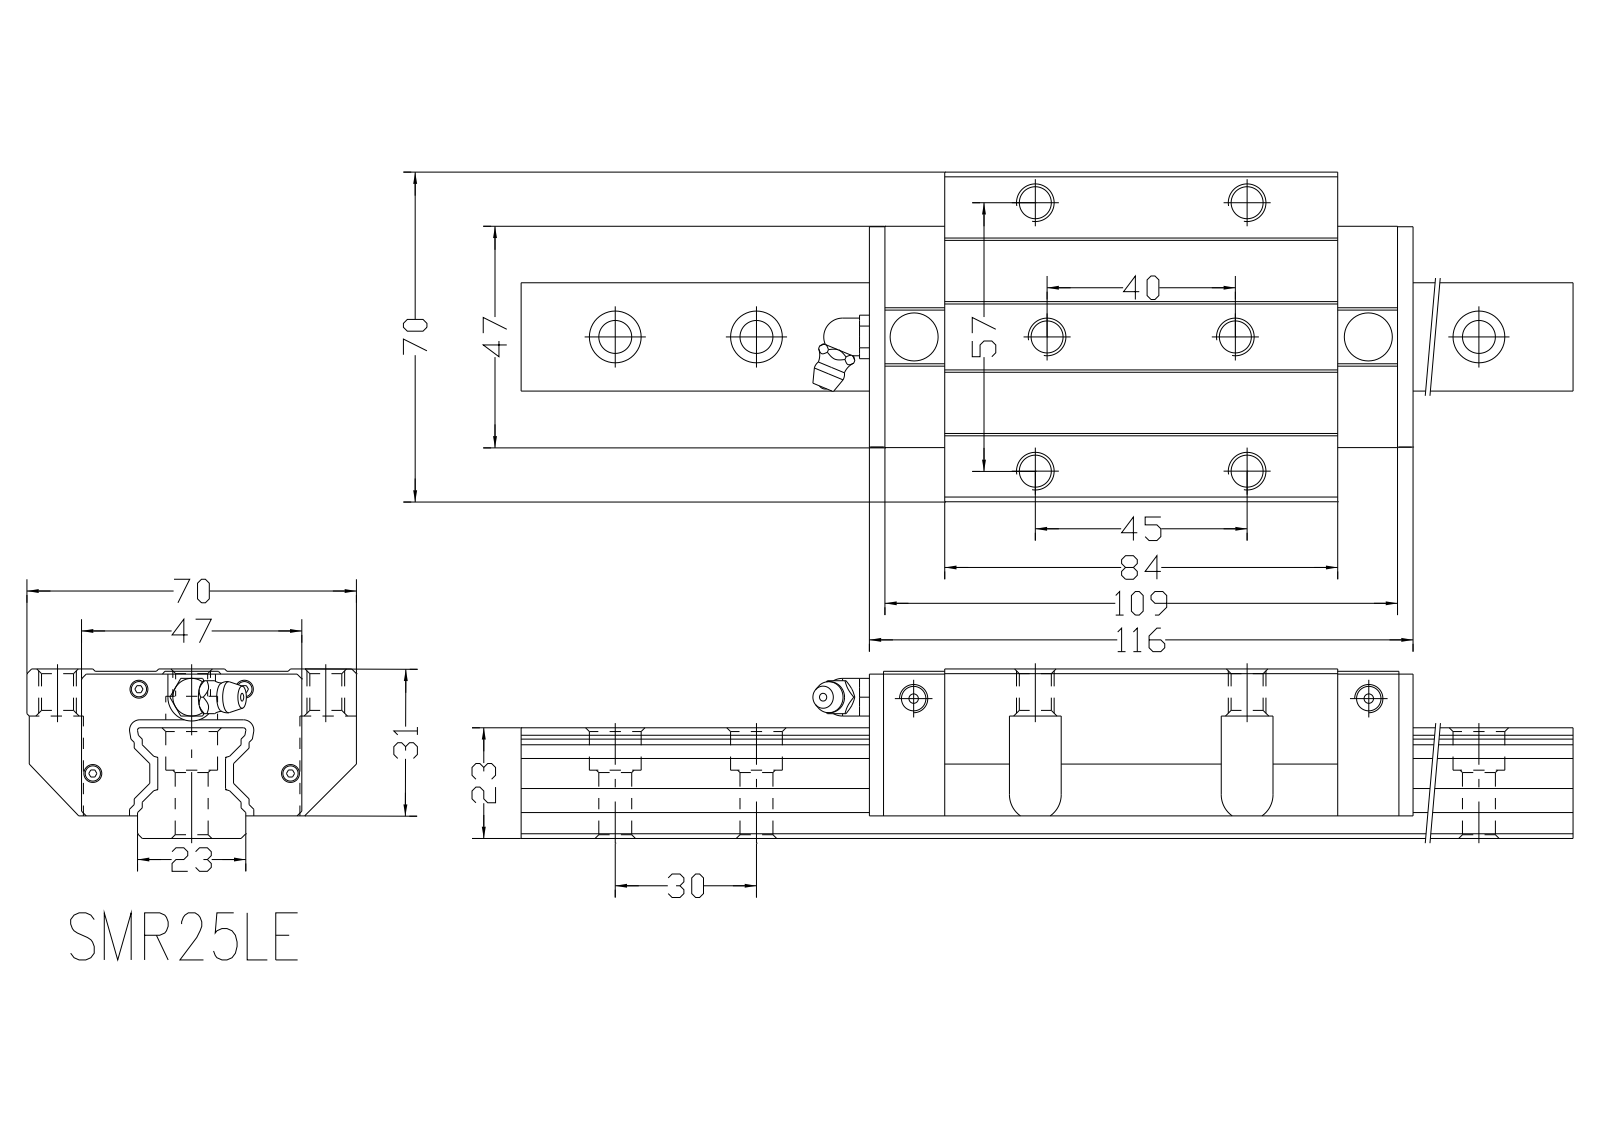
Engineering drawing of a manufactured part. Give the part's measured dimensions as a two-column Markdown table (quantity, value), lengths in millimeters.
| quantity | value |
| --- | --- |
| STEP written by | Kubotek KeyCreator V6.5.2 (0407) (CONFIG_CONTROL_DESIGN) |
| units | millimeters |
| bodies | 1 solid, 287 faces (156 planar, 90 cylindrical, 41 other) |
| overall size | 220 × 70 × 36 |
| volume | 797 mm³ |
| surface area | 57 236 mm² |
| round holes (diameter × count) | 7 × 7, 11 × 7, 7.2 × 6, 5.2 × 2, 10.2 × 2, 6.5 × 1 |
| round bosses / shafts (diameter × count) | 8 × 1 |
| partial cylindrical surfaces (radius × count) | 0.3 × 4, 5.5 × 4, 0.5 × 2, 5.1 × 1 |
| main face-to-face distances | 23.5, 18.7, 0.5, 12, 30.7, 36, 12.5, 11.5, 4.8, 31.2 |
| hole center spacings | 30, 60, 28.61, 38.41, 51.17, 76.27, 90, 120 |
